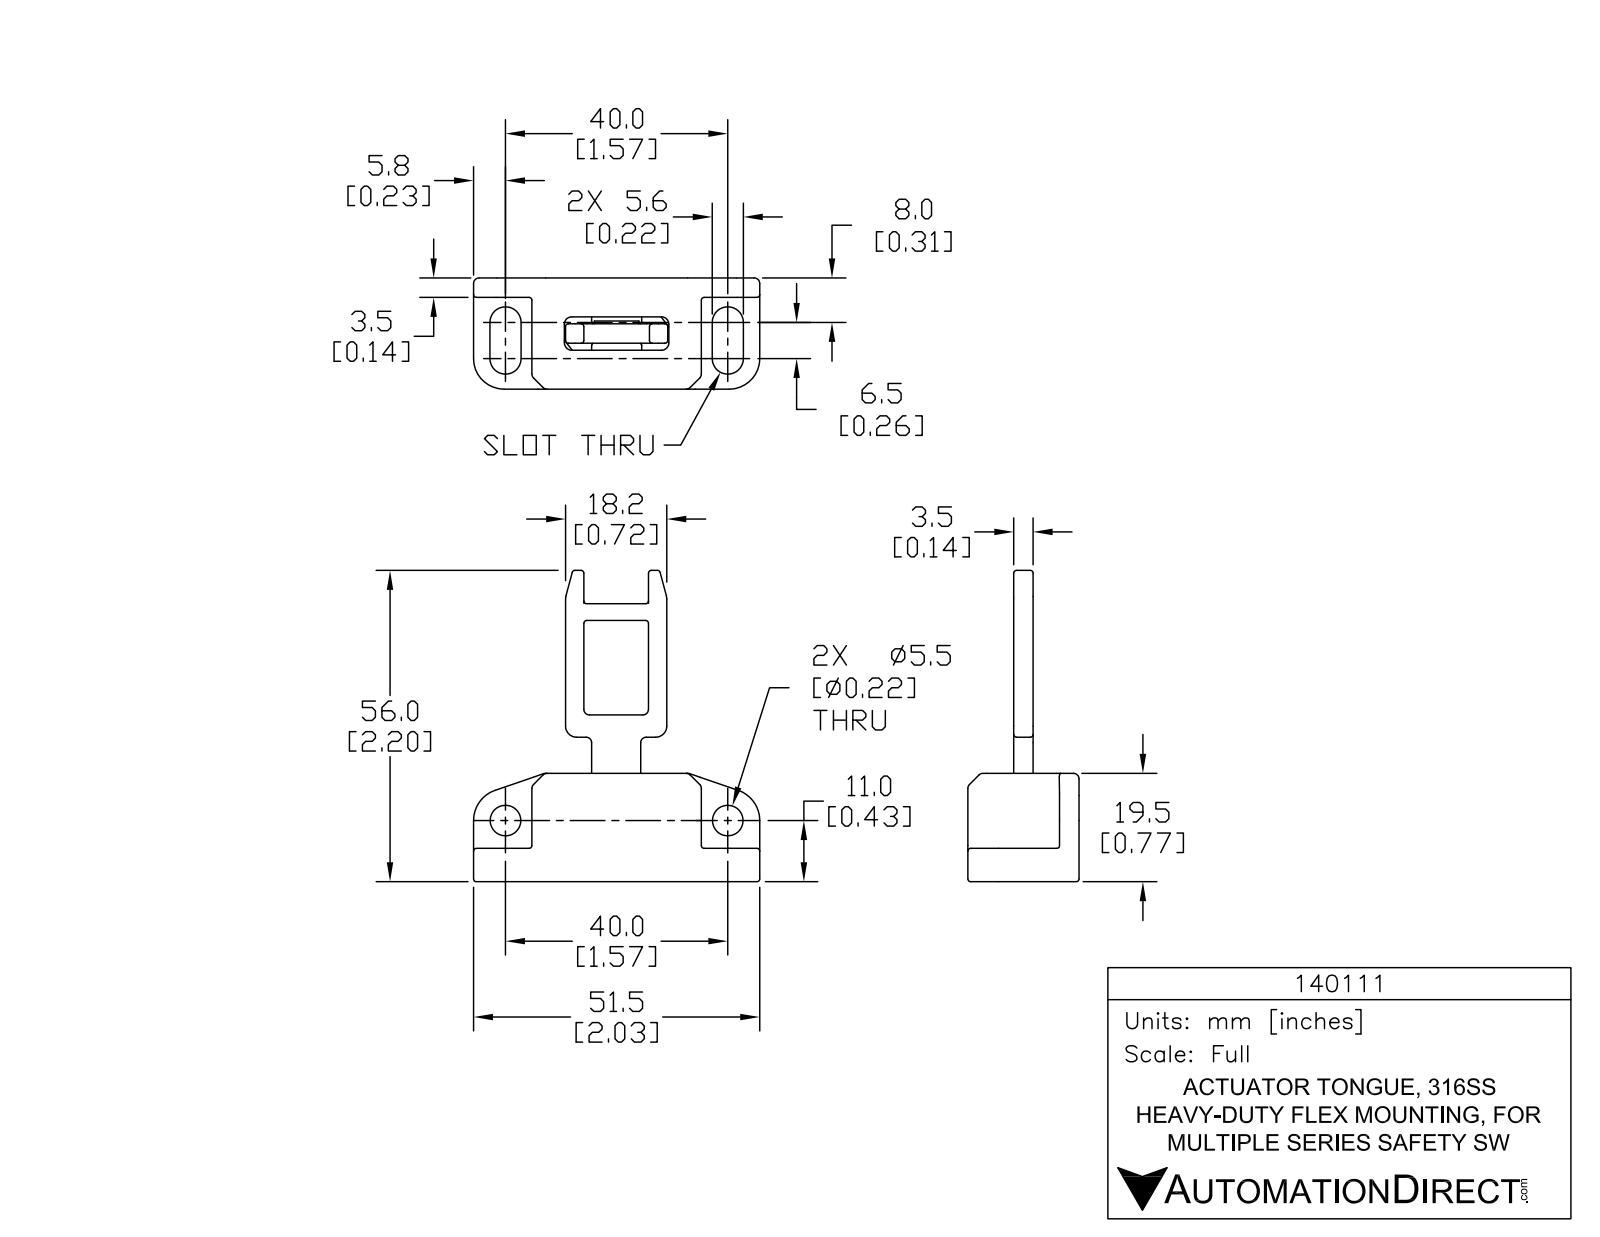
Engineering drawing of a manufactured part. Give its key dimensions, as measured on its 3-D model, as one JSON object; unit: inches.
{"part_name": "140111", "step_written_by": "SolidWorks 2017 (AUTOMOTIVE_DESIGN)", "units": "inches", "bodies": {"solids": 1, "faces": 289, "planar": 52, "cylindrical": 135, "other": 102}, "overall_size": [2.205, 2.028, 0.787], "volume_in3": 0.887, "surface_area_in2": 9.071, "round_holes": [[0.217, 2]], "partial_cylinders_radius": [[0.02, 74], [0.039, 29], [0.051, 4], [0.079, 4], [0.11, 4], [0.031, 2], [0.217, 2], [0.226, 2]], "face_to_face_distances": [0.325, 0.463, 0.787, 0.138, 0.413, 0.748, 0.02, 0.768, 0.65, 1.614], "hole_center_spacings": [1.575]}
